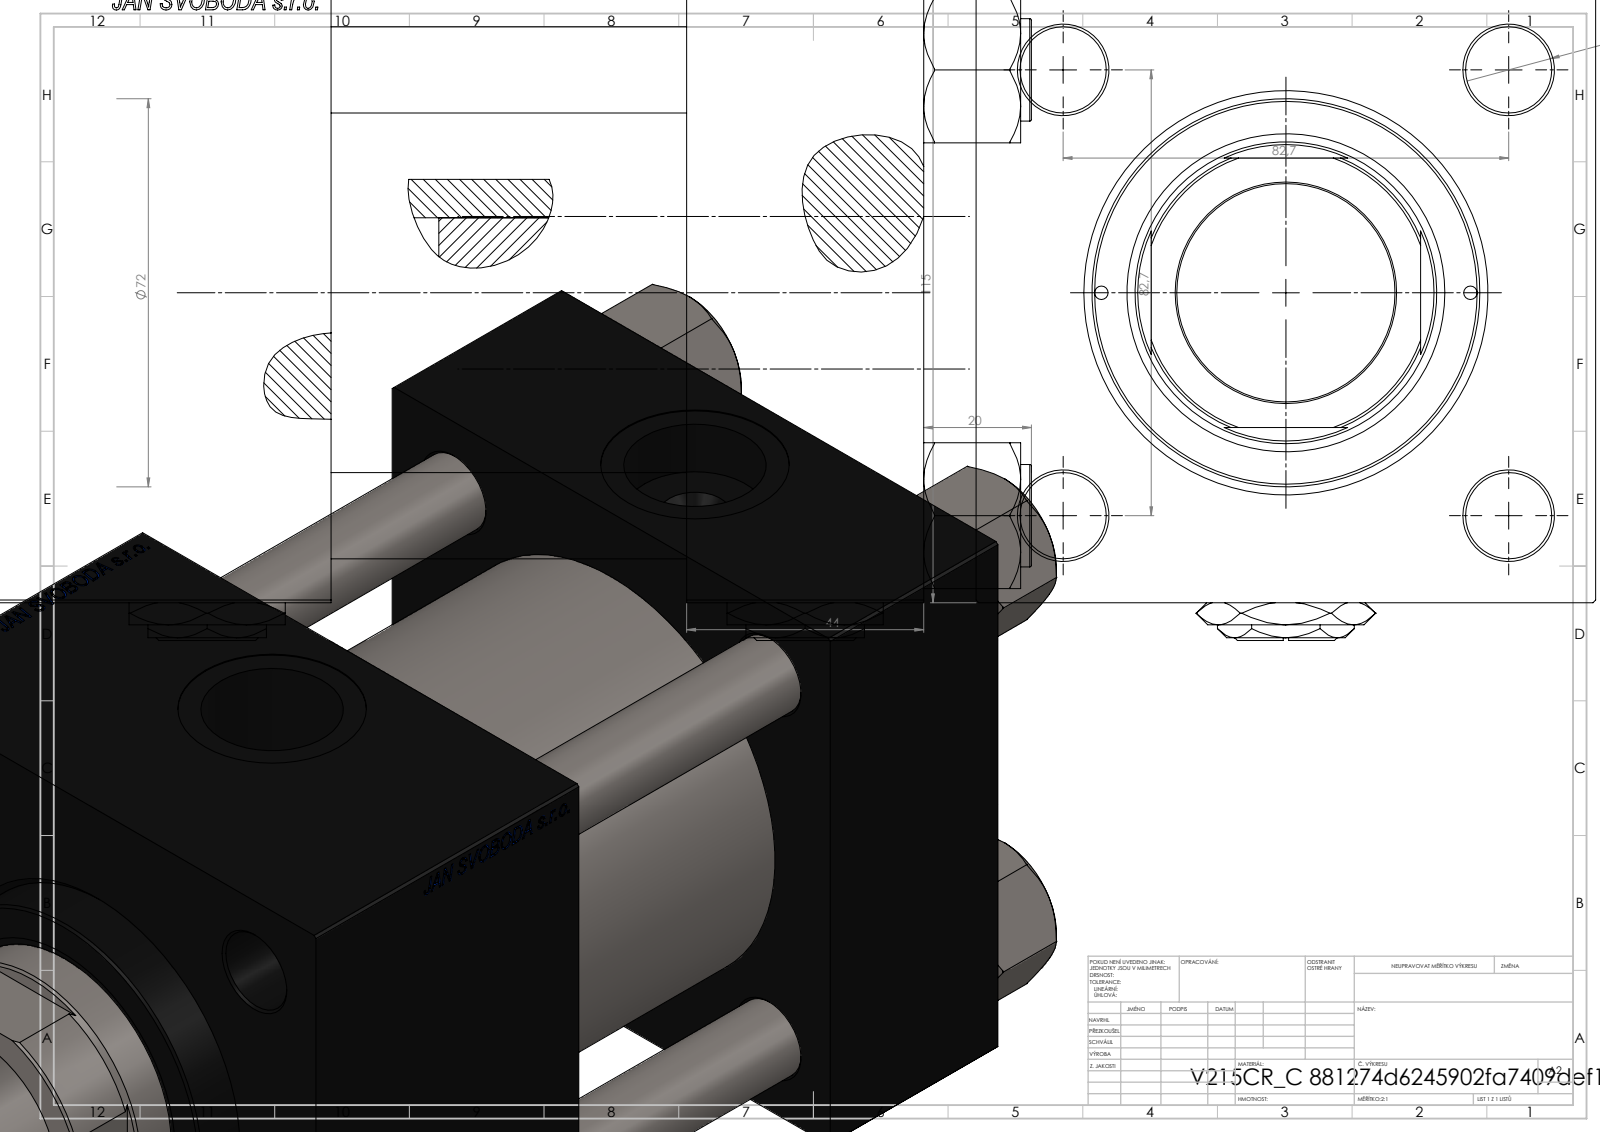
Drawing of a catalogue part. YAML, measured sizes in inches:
part_name: "V215CR_VCP_C; V215_VC_A; V215CR_C_TYCINKA; V215CR_C_Body (+2 more)"
step_written_by: "SolidWorks 2019 (CONFIG_CONTROL_DESIGN)"
units: inches
bodies: {solids: 13, faces: 1300, planar: 622, cylindrical: 100, other: 578}
overall_size: [9.055, 4.803, 4.528]
volume: 112.7
surface_area: 445.6
round_holes:
  - {diameter: 0.63, count: 4}
  - {diameter: 0.098, count: 2}
  - {diameter: 0.276, count: 2}
  - {diameter: 1.041, count: 2}
  - {diameter: 1.378, count: 2}
  - {diameter: 1.594, count: 1}
  - {diameter: 2.205, count: 1}
  - {diameter: 2.323, count: 1}
  - {diameter: 2.402, count: 1}
  - {diameter: 2.835, count: 1}
  - {diameter: 3.15, count: 1}
round_bosses_or_shafts:
  - {diameter: 0.748, count: 4}
  - {diameter: 3.386, count: 1}
partial_cylinders:
  - {radius: 1.063, count: 1}
face_to_face_distances: [4.528, 1.732, 4.331, 2.598, 2.717, 7.047, 5.315, 0.787, 4.52, 5.917]
hole_center_spacings: [1.652, 2.302, 3.256, 3.393, 1.348, 4.605, 2.697, 4.37]
